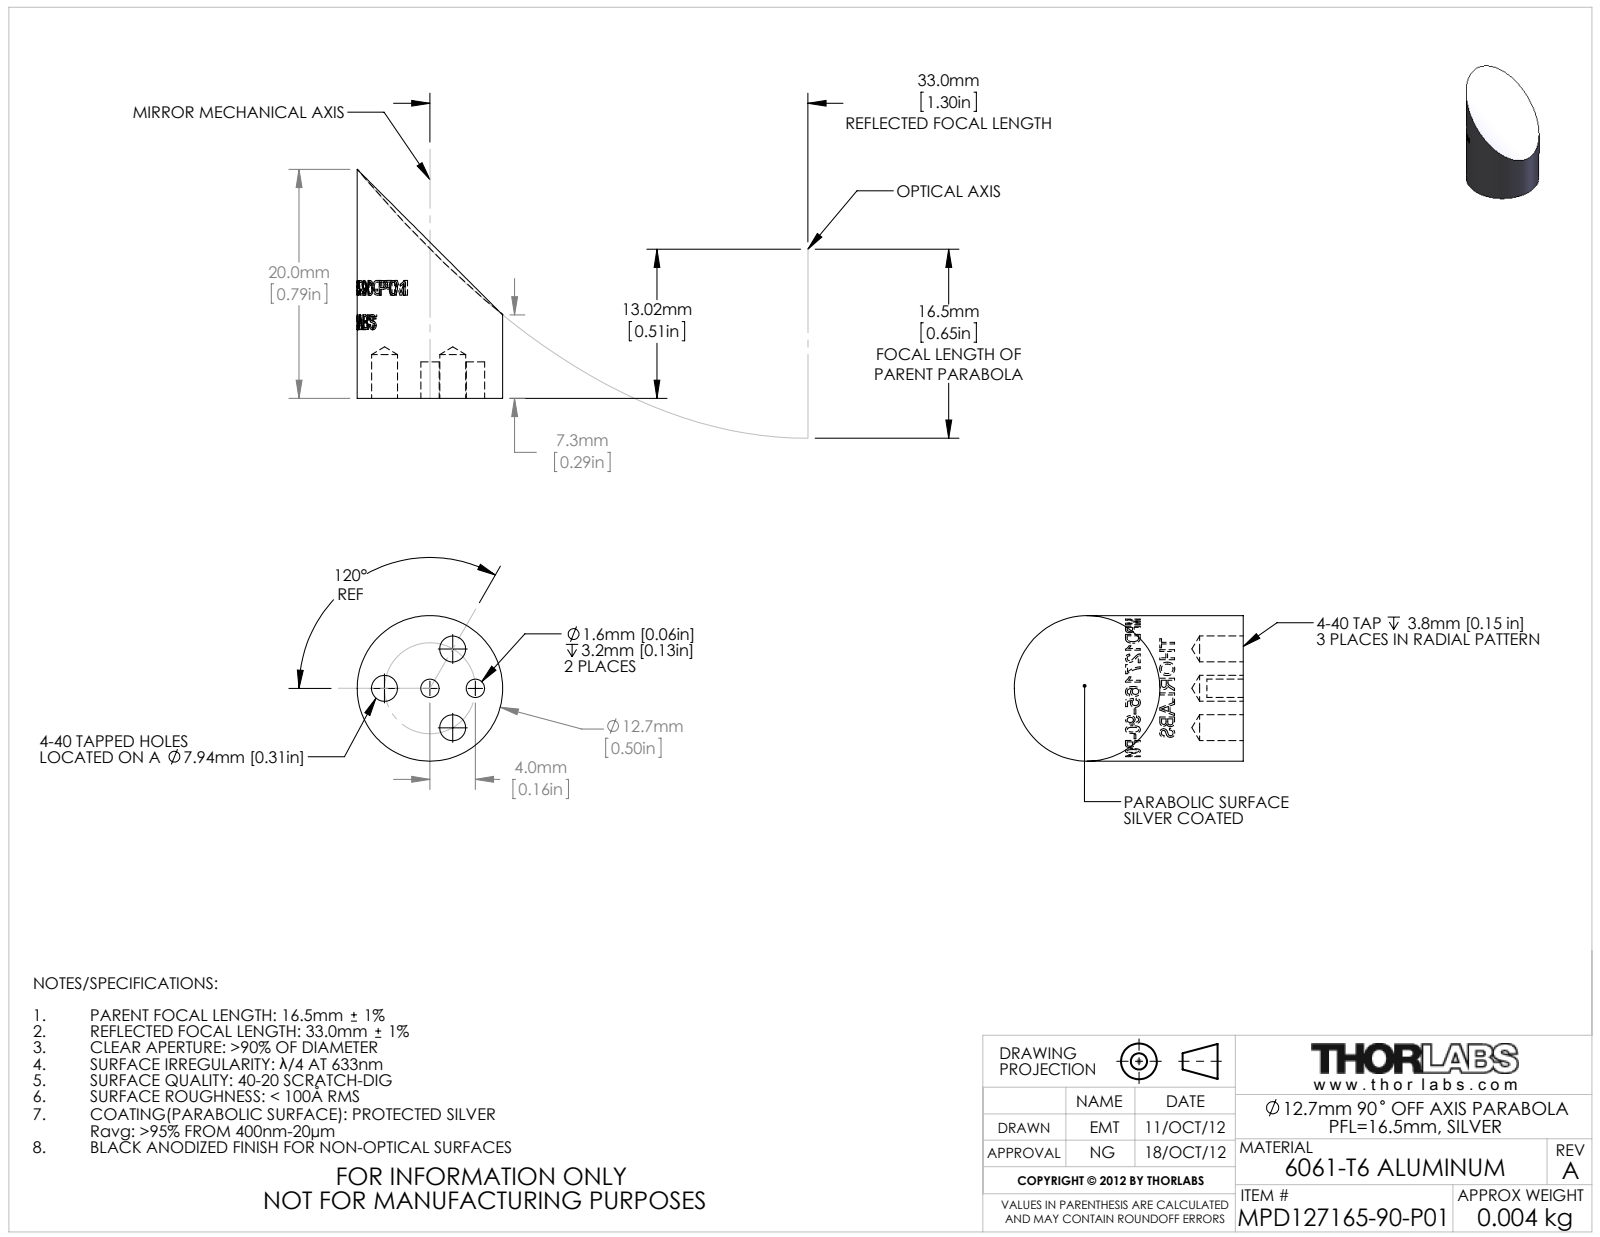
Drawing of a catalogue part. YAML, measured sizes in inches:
part_name: "TTN005552-E0W"
step_written_by: "SolidWorks 2012 (CONFIG_CONTROL_DESIGN)"
units: inches
bodies: {solids: 1, faces: 60, planar: 3, cylindrical: 49, other: 8}
overall_size: [0.787, 0.5, 0.5]
volume: 0.099
surface_area: 1.496
round_holes:
  - {diameter: 0.089, count: 3}
  - {diameter: 0.063, count: 2}
round_bosses_or_shafts:
  - {diameter: 0.5, count: 1}
face_to_face_distances: [0.125]
hole_center_spacings: [0.156, 0.27, 0.271, 0.313]
